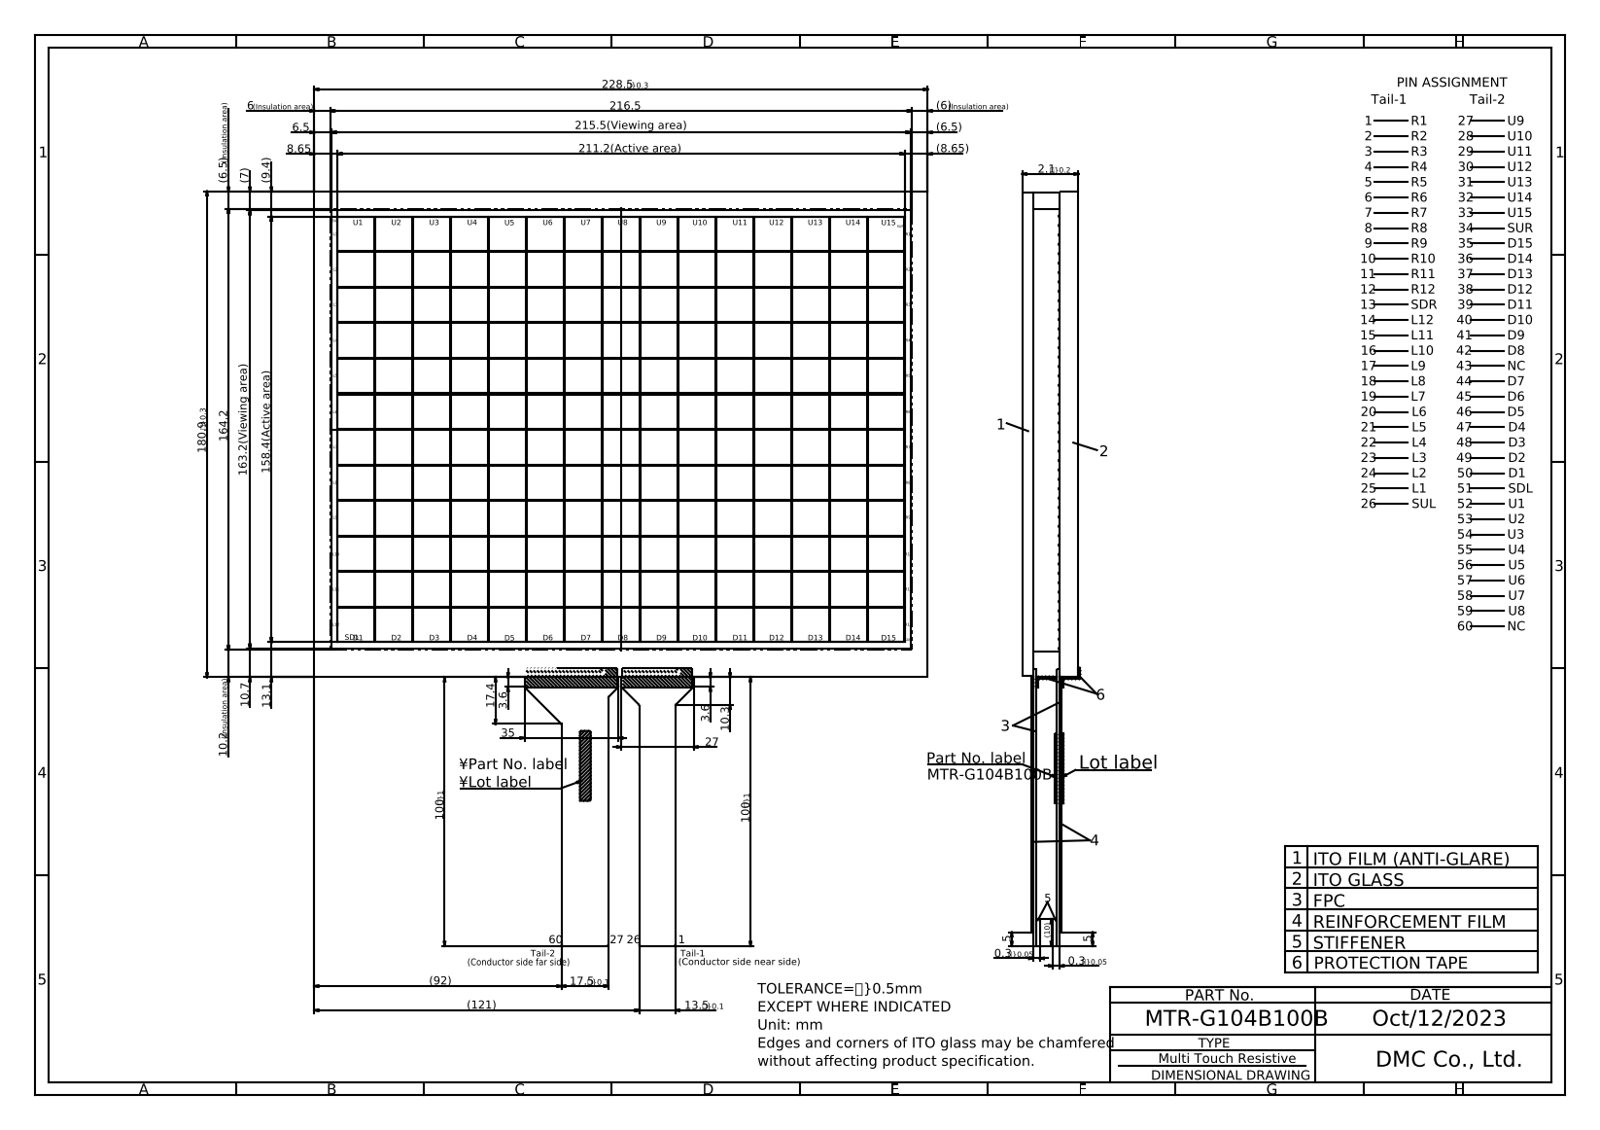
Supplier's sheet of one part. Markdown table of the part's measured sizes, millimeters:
| quantity | value |
| --- | --- |
| part name | MTR-G104B100B |
| STEP written by | Autodesk Inventor 2020 (CONFIG_CONTROL_DESIGN) |
| units | millimeters |
| bodies | 1 solid, 294 faces (282 planar, 12 cylindrical, 0 other) |
| overall size | 319.9 × 317.08 × 2.2 |
| volume | 87 046 mm³ |
| surface area | 91 331 mm² |
| partial cylindrical surfaces (radius × count) | 1 × 8, 0.2 × 4 |
| main face-to-face distances | 2.1, 1.8, 1.9, 2, 180.9, 228.5, 0.4, 2.2, 0.5, 0.7 |
